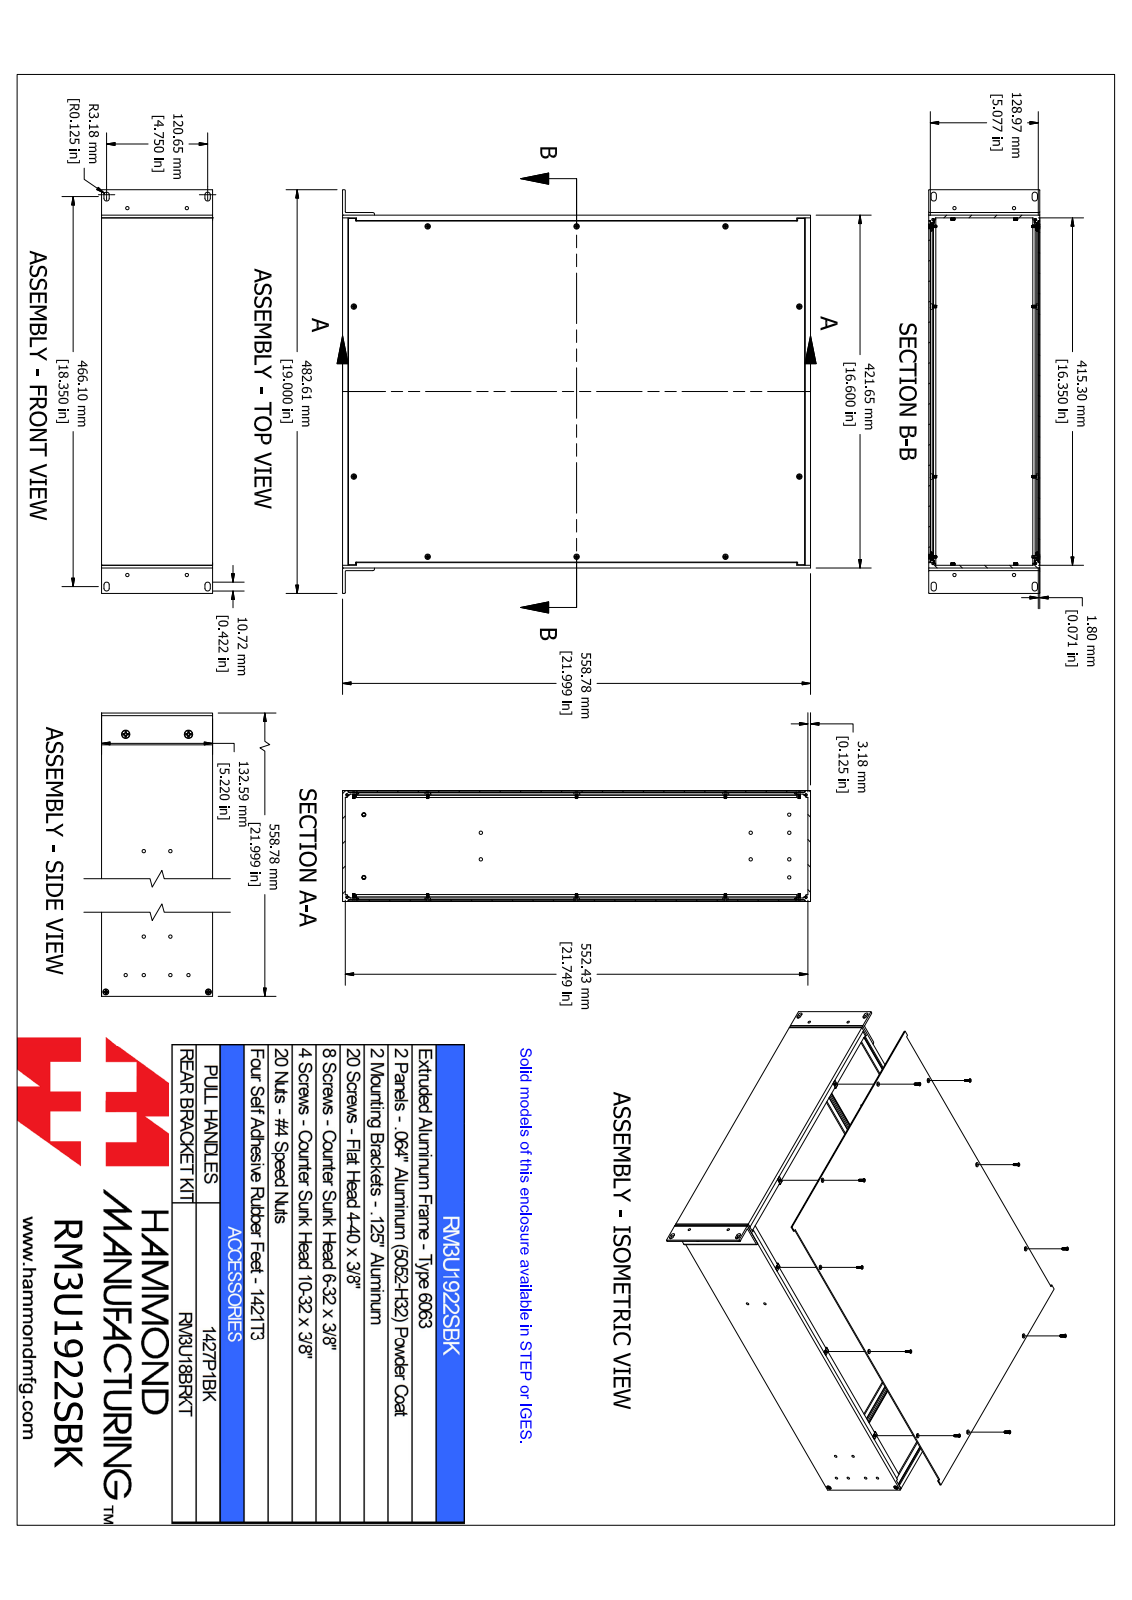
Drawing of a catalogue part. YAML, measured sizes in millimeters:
part_name: "RM3U1922SBK"
step_written_by: "SolidWorks 2021 (AUTOMOTIVE_DESIGN)"
units: millimeters
bodies: {solids: 60, faces: 2284, planar: 952, cylindrical: 544, other: 788}
overall_size: [560.4, 482.6, 132.6]
volume: 1835000
surface_area: 1594000
round_holes:
  - {diameter: 4, count: 10}
  - {diameter: 4.1, count: 10}
  - {diameter: 4, count: 6}
  - {diameter: 4.2, count: 6}
  - {diameter: 3.5, count: 4}
  - {diameter: 4, count: 4}
  - {diameter: 4, count: 4}
  - {diameter: 4.3, count: 4}
  - {diameter: 5, count: 2}
round_bosses_or_shafts:
  - {diameter: 5.1, count: 10}
  - {diameter: 2.8, count: 10}
  - {diameter: 6, count: 6}
  - {diameter: 3.5, count: 6}
  - {diameter: 9.1, count: 2}
  - {diameter: 4.8, count: 2}
partial_cylinders:
  - {radius: 0.3, count: 80}
  - {radius: 0.6, count: 80}
  - {radius: 0.2, count: 40}
  - {radius: 0.4, count: 40}
  - {radius: 0.4, count: 16}
  - {radius: 1, count: 16}
  - {radius: 1, count: 14}
  - {radius: 0.9, count: 9}
face_to_face_distances: [130.8, 1.8, 132.6, 129, 418.5, 3.2, 3.2, 555.6, 421.7, 415.3]
hole_center_spacings: [177.8, 130.2, 433, 203.2, 282.7, 400.2, 311.8, 454]
